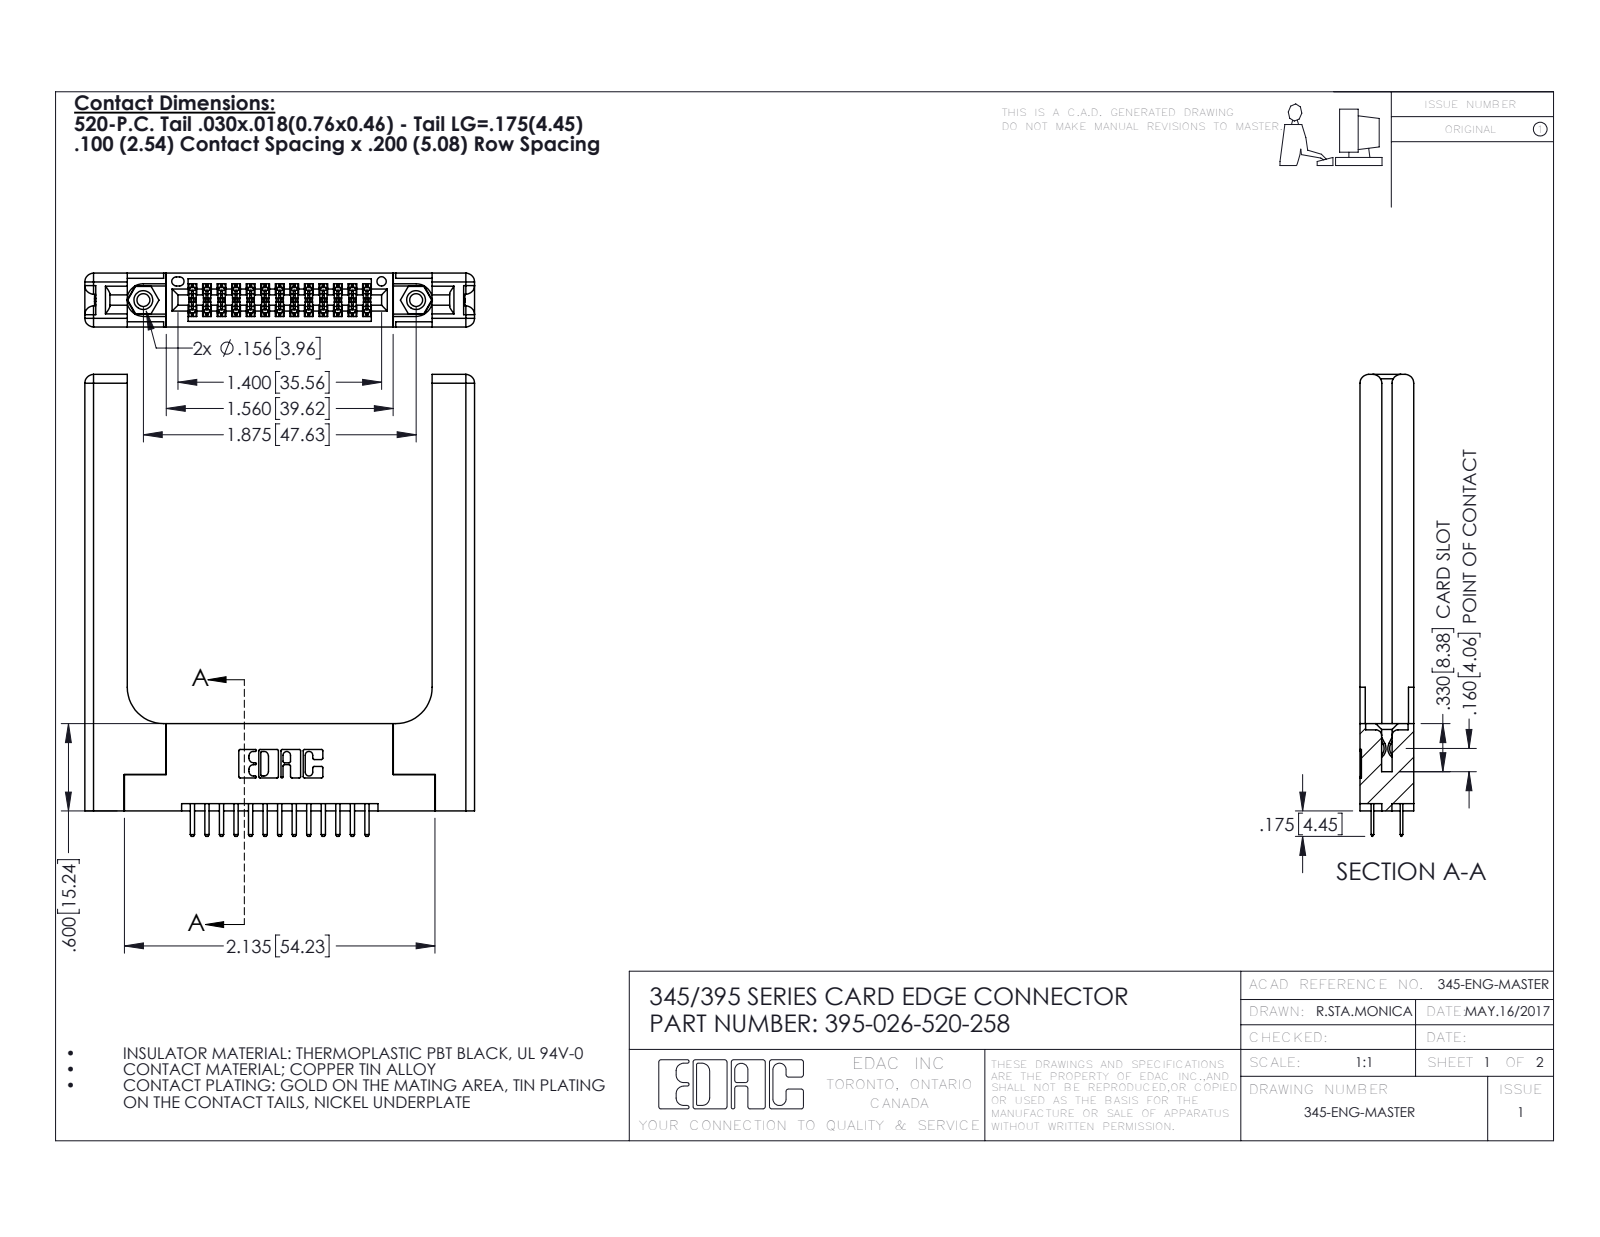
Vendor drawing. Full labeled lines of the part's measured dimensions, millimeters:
Part name (STEP PRODUCT): 395-026-520-258; 345-250-001_345-250-001-102; 345-220-058_345-220-058; 345-292-001_345-293-120 (+1 more)
STEP written by: SolidWorks 2016 (CONFIG_CONTROL_DESIGN)
Units: millimetres
Bodies: 31 solids, 1786 faces (1138 planar, 588 cylindrical, 60 other)
Overall size (bounding box): 80.6 × 68 × 9.4
Volume: 14 800 mm³ · Surface area: 13 830 mm²
Round holes (diameter × count): ⌀2.3 ×2, ⌀3.2 ×2, ⌀4 ×2, ⌀1.6 ×1
Round bosses / shafts (diameter × count): ⌀3.9 ×2
Partial cylindrical surfaces — rounded edges, fillets, slot ends (radius × count): R0.2 ×39, R0.3 ×30, R0.3 ×22, R1.5 ×16, R0.2 ×6, R0.8 ×6, R0.7 ×3, R0.4 ×2
Main face-to-face distances: 9.4, 1.8, 7.6, 5.1, 2, 3.8, 5.6, 3.8, 5.7, 53.2
Hole centre spacings: 6.9, 41.7, 47.6
